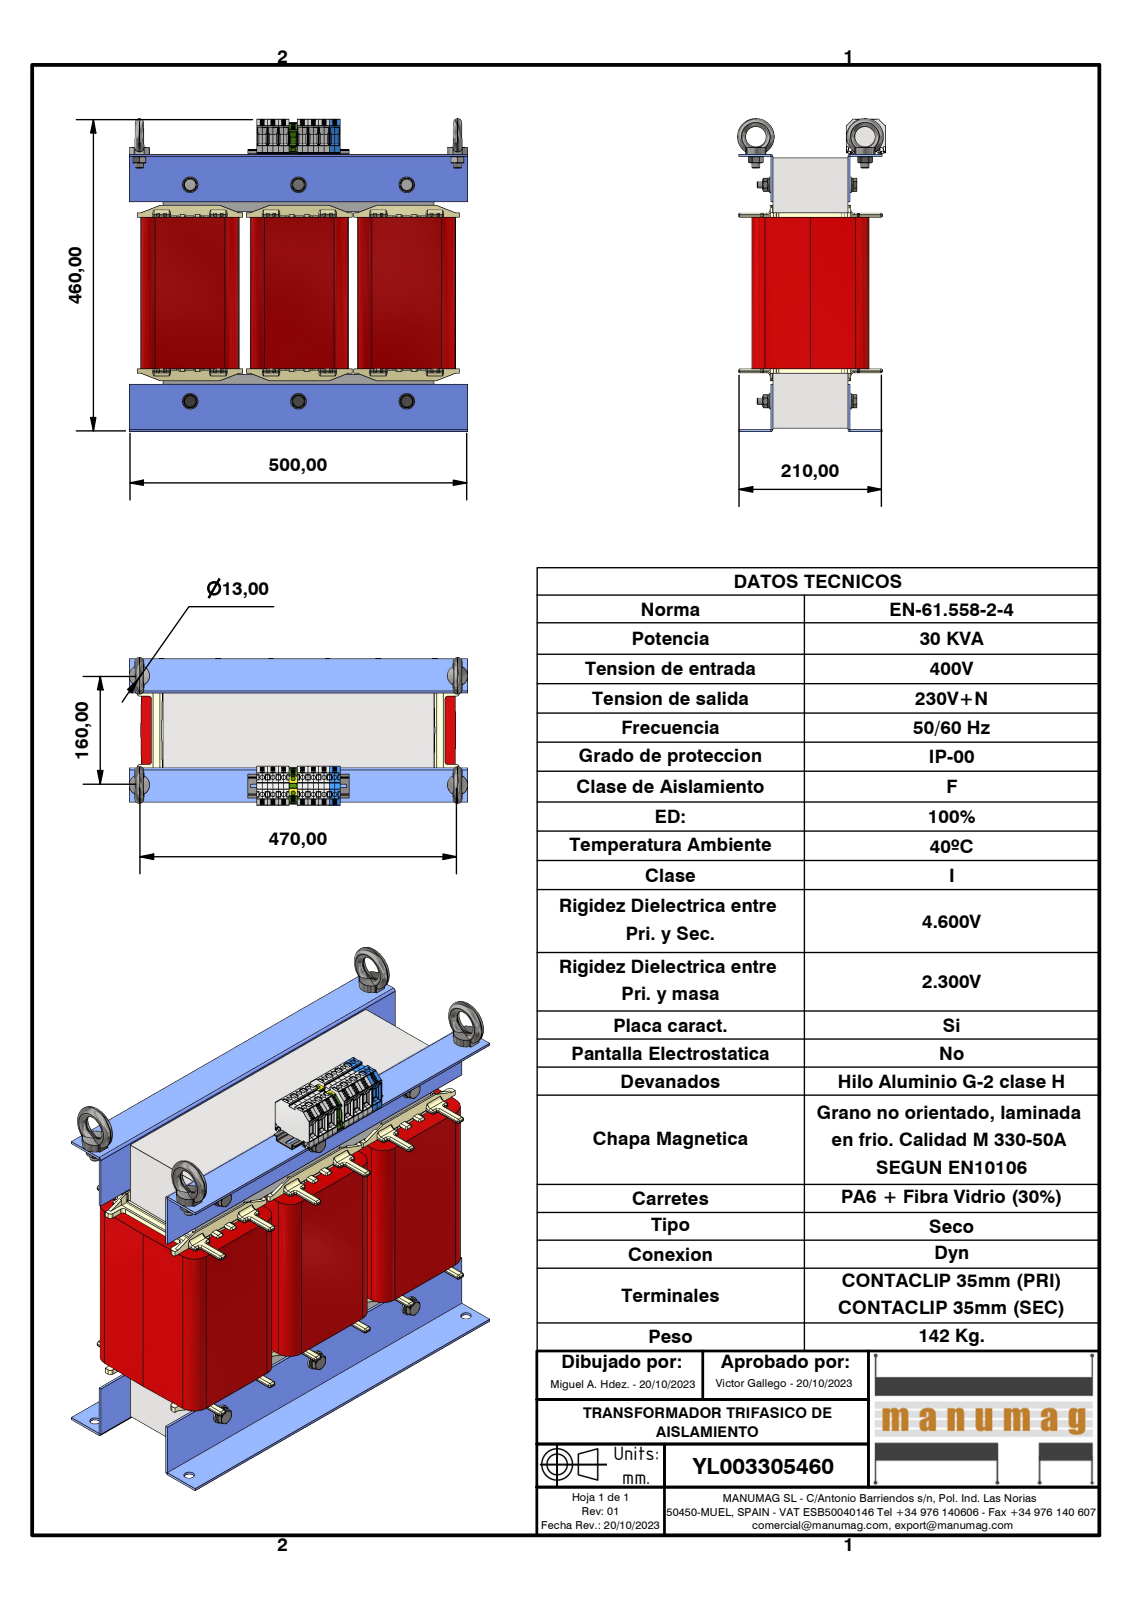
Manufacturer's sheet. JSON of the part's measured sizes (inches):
{"part_name": "YL003305460; 3UI240 400 x 400 - 110; UI 240_110_BOBINADO; RC80 NT080 (+8 more)", "step_written_by": "Autodesk Inventor 2023 (AUTOMOTIVE_DESIGN)", "units": "inches", "bodies": {"solids": 61, "faces": 8997, "planar": 4919, "cylindrical": 2672, "other": 1406}, "overall_size": [19.685, 18.228, 8.555], "volume_in3": 1490, "surface_area_in2": 4174, "round_holes": [[0.256, 14], [0.512, 10], [0.33, 6], [0.394, 6], [0.413, 6], [0.591, 6], [0.079, 4], [0.398, 4], [0.248, 2], [1.181, 2]], "round_bosses_or_shafts": [[0.024, 12], [0.906, 6], [0.787, 6], [0.606, 6], [0.453, 6], [0.362, 6], [0.472, 4], [0.425, 4]], "partial_cylinders_radius": [[0.012, 494], [0.079, 202], [0.02, 188], [0.039, 90], [0.01, 34], [0.032, 33], [0.075, 32], [0.157, 26]], "face_to_face_distances": [0.118, 12.598, 4.331, 0.236, 1.215, 4.449, 4.567, 0.079, 4.575, 0.978], "hole_center_spacings": [0.626, 1.167, 0.984, 6.299, 1.252, 1.593, 2.346, 2.544]}
